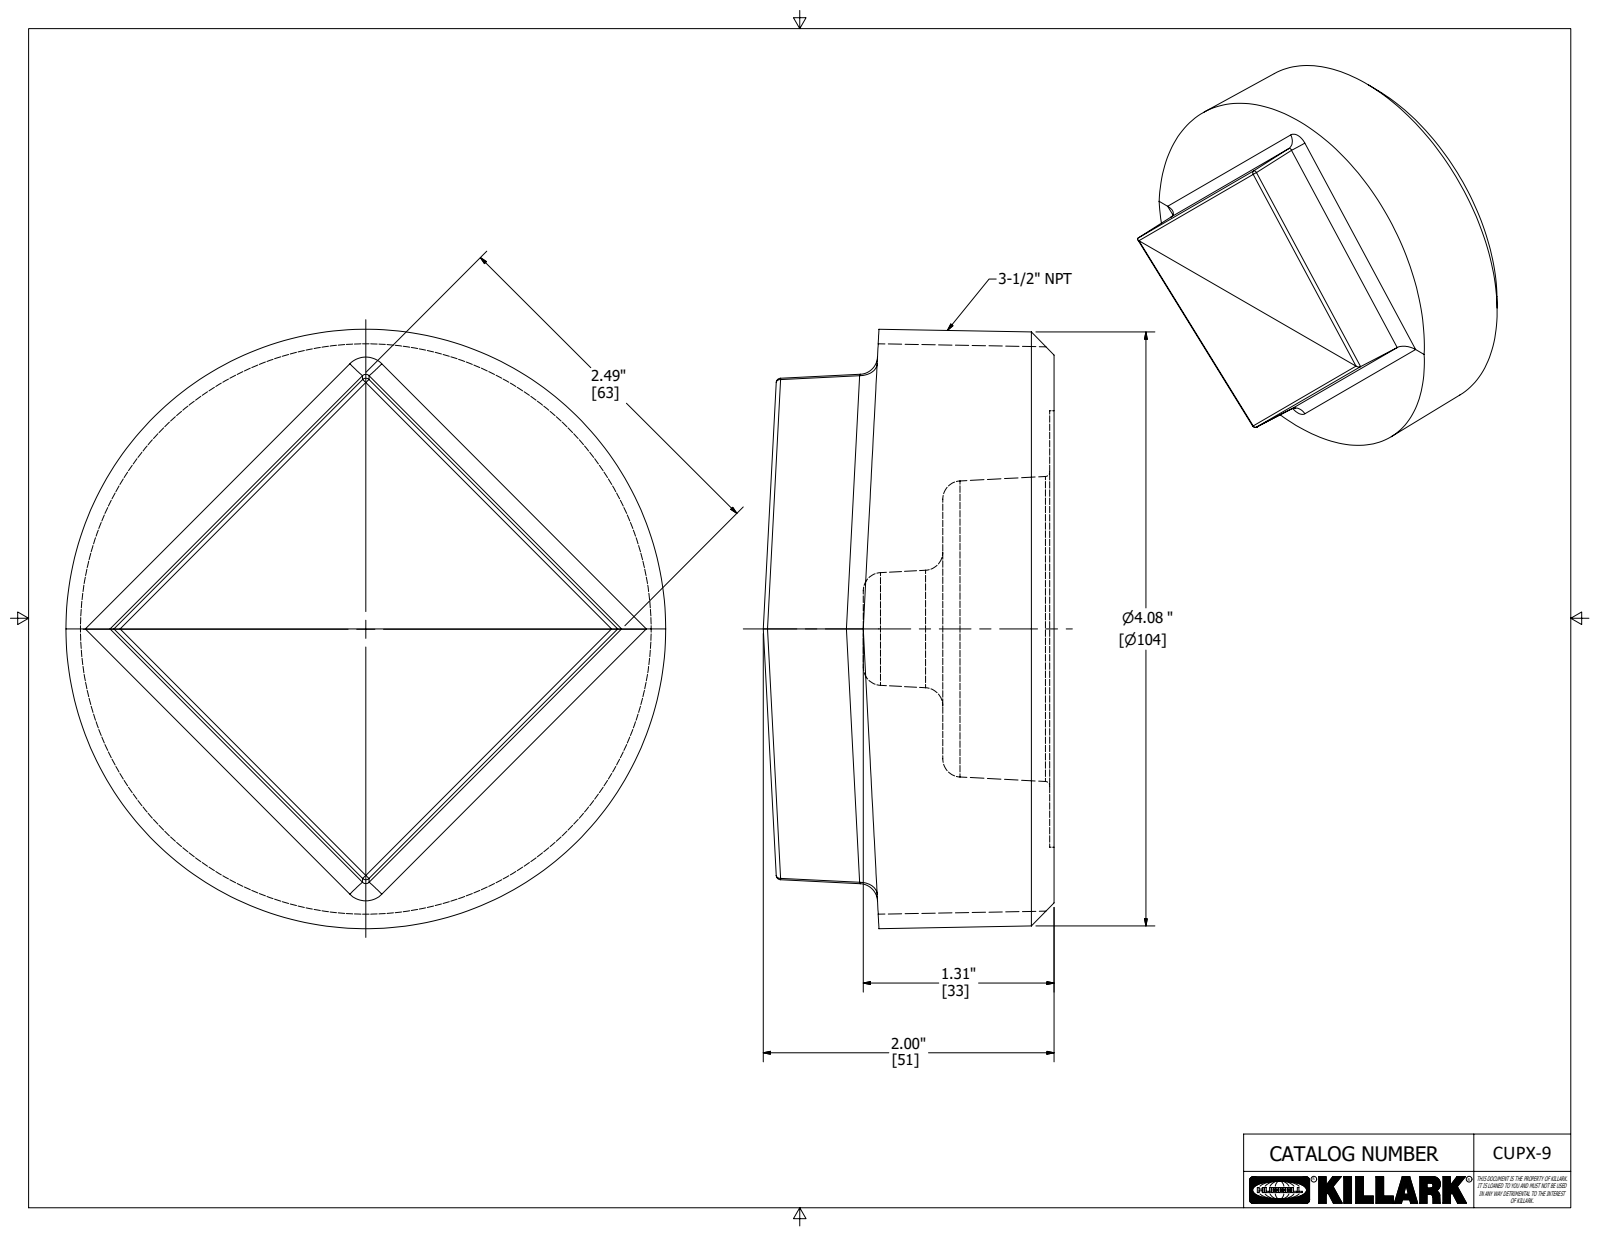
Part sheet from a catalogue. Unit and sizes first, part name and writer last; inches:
Units: inches
Overall size (bounding box): 4.125 × 4.121 × 2
Round holes (diameter × count): ⌀3 ×1
Partial cylindrical surfaces — rounded edges, fillets, slot ends (radius × count): R0.031 ×6, R0.125 ×4
Main face-to-face distances: 0.03, 0.687, 0.687, 0.736, 0.766, 0.547, 1.283, 1.313
Volume: 17.89 in³ · Surface area: 52.75 in²
Bodies: 1 solid, 35 faces (12 planar, 11 cylindrical, 12 other)
Part name (STEP PRODUCT): CUPX-9
STEP written by: Autodesk Inventor 2020 (AUTOMOTIVE_DESIGN)
